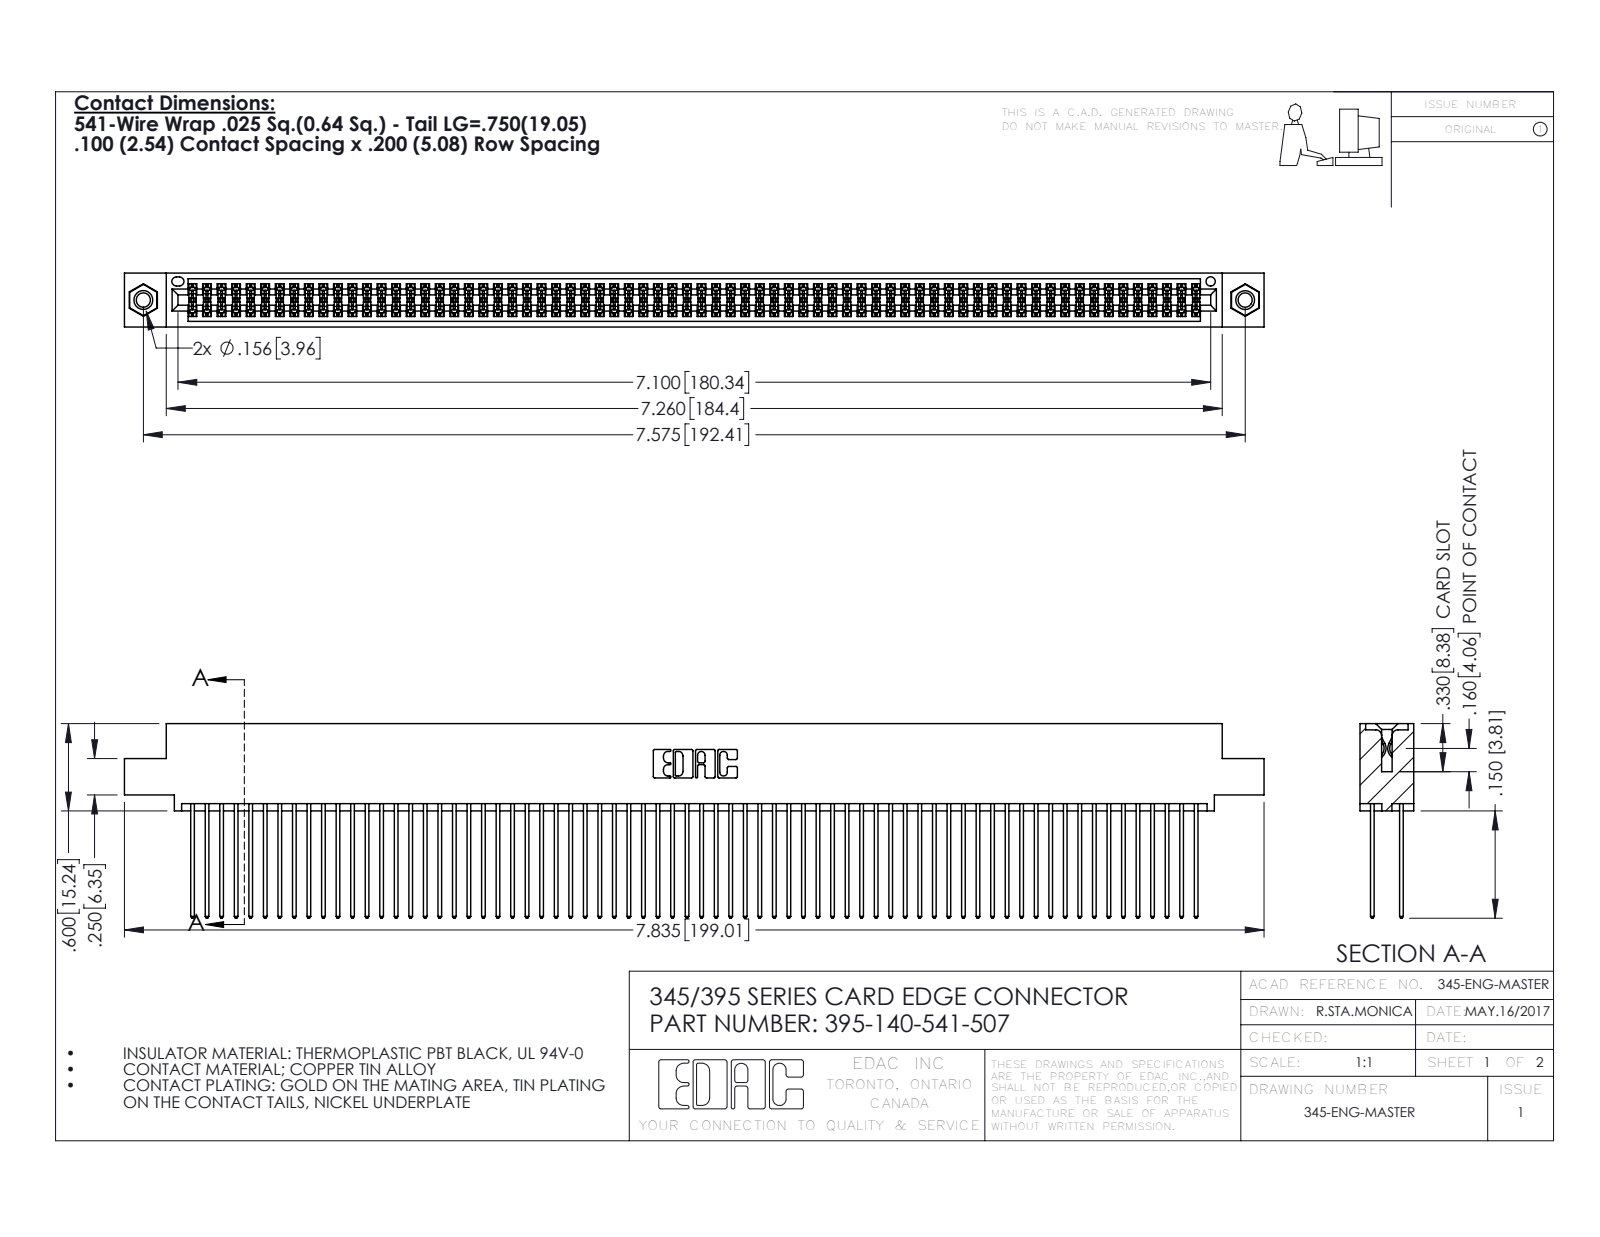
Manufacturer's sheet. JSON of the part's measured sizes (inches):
{"part_name": "345-292-001_345-293-141; 345-250-001_345-250-005-103; 345 Part_0.110 Offset - 0.156 Dia-TI; 395-140-541-507", "step_written_by": "SolidWorks 2016 (CONFIG_CONTROL_DESIGN)", "units": "inches", "bodies": {"solids": 143, "faces": 7190, "planar": 4736, "cylindrical": 2438, "other": 16}, "overall_size": [7.835, 1.337, 0.37], "volume_in3": 1.239, "surface_area_in2": 53.41, "round_holes": [[0.098, 2], [0.125, 2], [0.156, 2], [0.064, 1]], "round_bosses_or_shafts": [[0.155, 2]], "partial_cylinders_radius": [[0.006, 210], [0.01, 140], [0.01, 22], [0.007, 6], [0.031, 6], [0.026, 3], [0.014, 2], [0.019, 2]], "face_to_face_distances": [0.072, 0.298, 0.2, 0.098, 0.272, 0.025, 0.225, 0.37, 0.175, 0.149], "hole_center_spacings": [0.27, 7.339, 7.575]}
